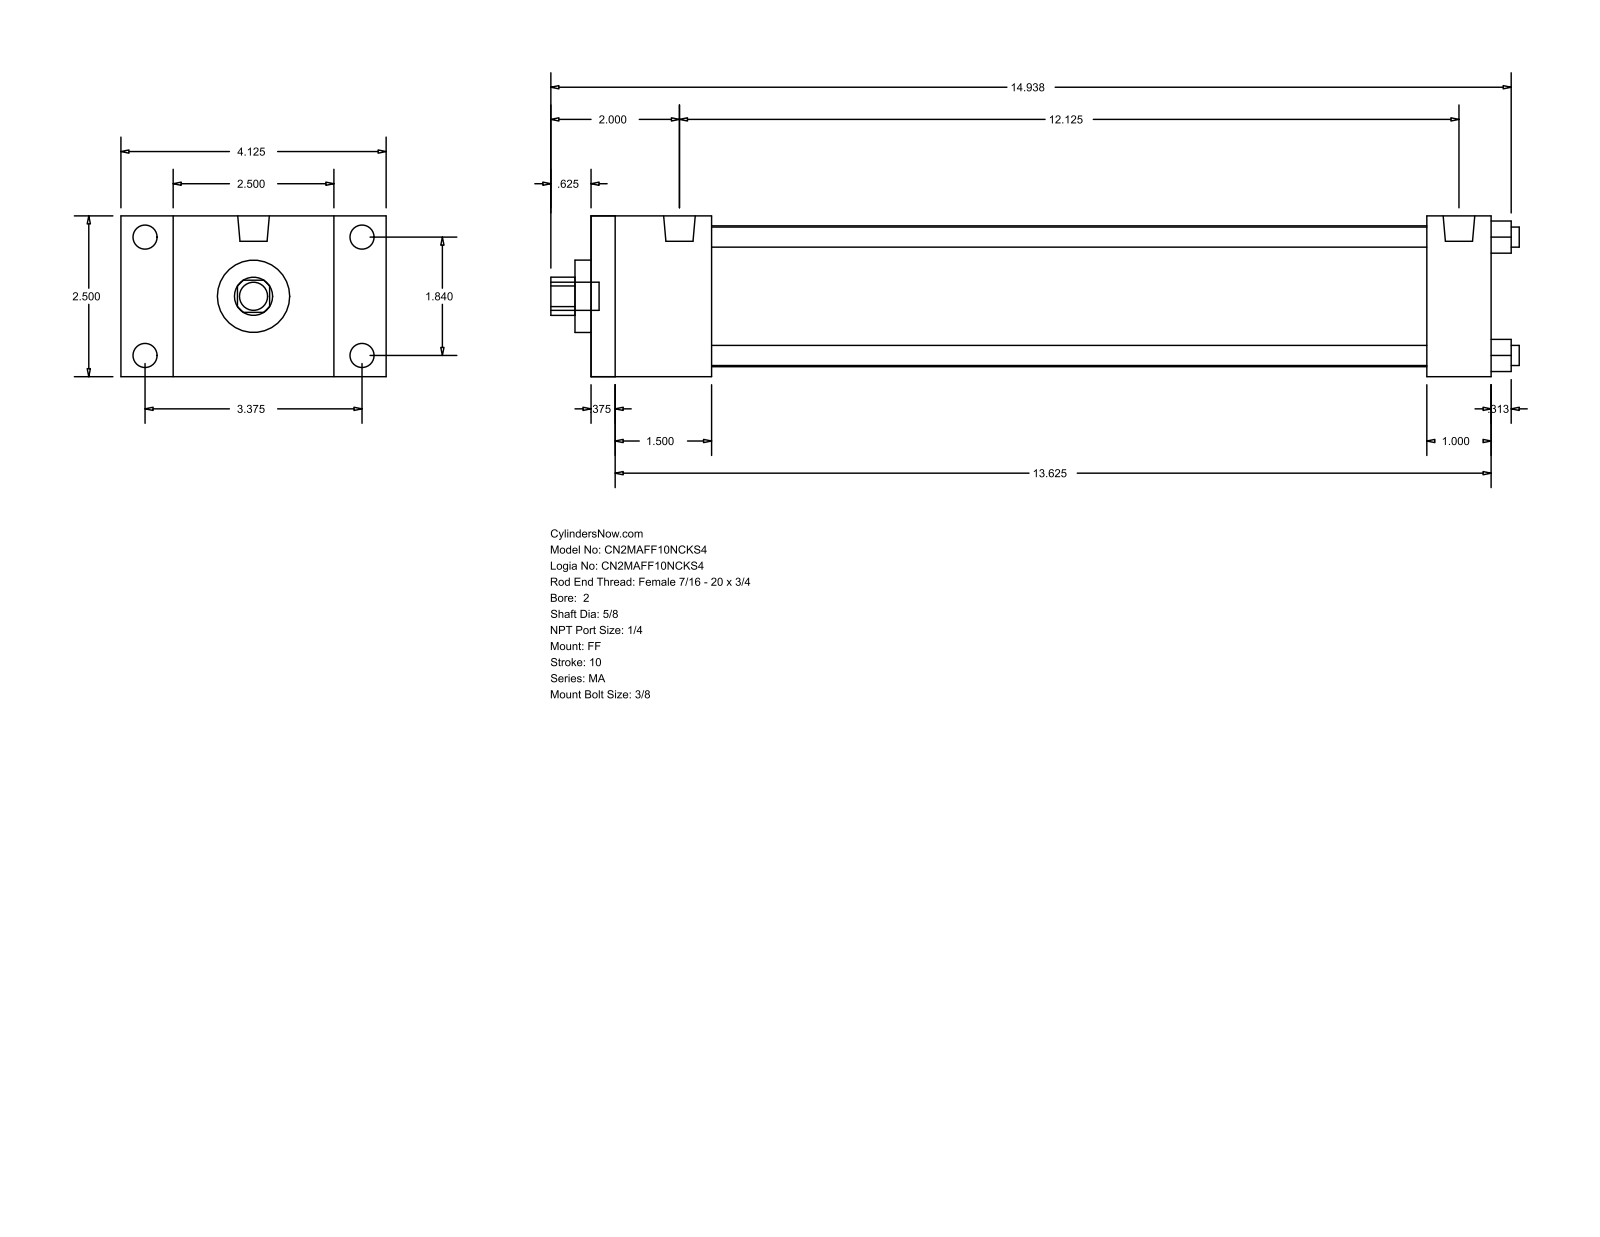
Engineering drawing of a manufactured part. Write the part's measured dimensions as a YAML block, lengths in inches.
part_name: "MA_FF__0200_0.625"
step_written_by: "GSSL Pune (CONFIG_CONTROL_DESIGN)"
units: inches
bodies: {solids: 0, faces: 92, planar: 64, cylindrical: 28, other: 0}
overall_size: [15.063, 4.125, 2.5]
round_holes:
  - {diameter: 0.313, count: 4}
  - {diameter: 0.625, count: 1}
  - {diameter: 1.125, count: 1}
  - {diameter: 2.19, count: 1}
round_bosses_or_shafts:
  - {diameter: 0.375, count: 4}
  - {diameter: 0.313, count: 4}
  - {diameter: 0.492, count: 2}
  - {diameter: 0.437, count: 1}
partial_cylinders:
  - {radius: 0.297, count: 1}
face_to_face_distances: [2.5, 14, 0.375, 13.625, 1.5, 1.875, 13, 12.625, 11.125, 12.125]
hole_center_spacings: [1.301, 1.84, 2.602]
